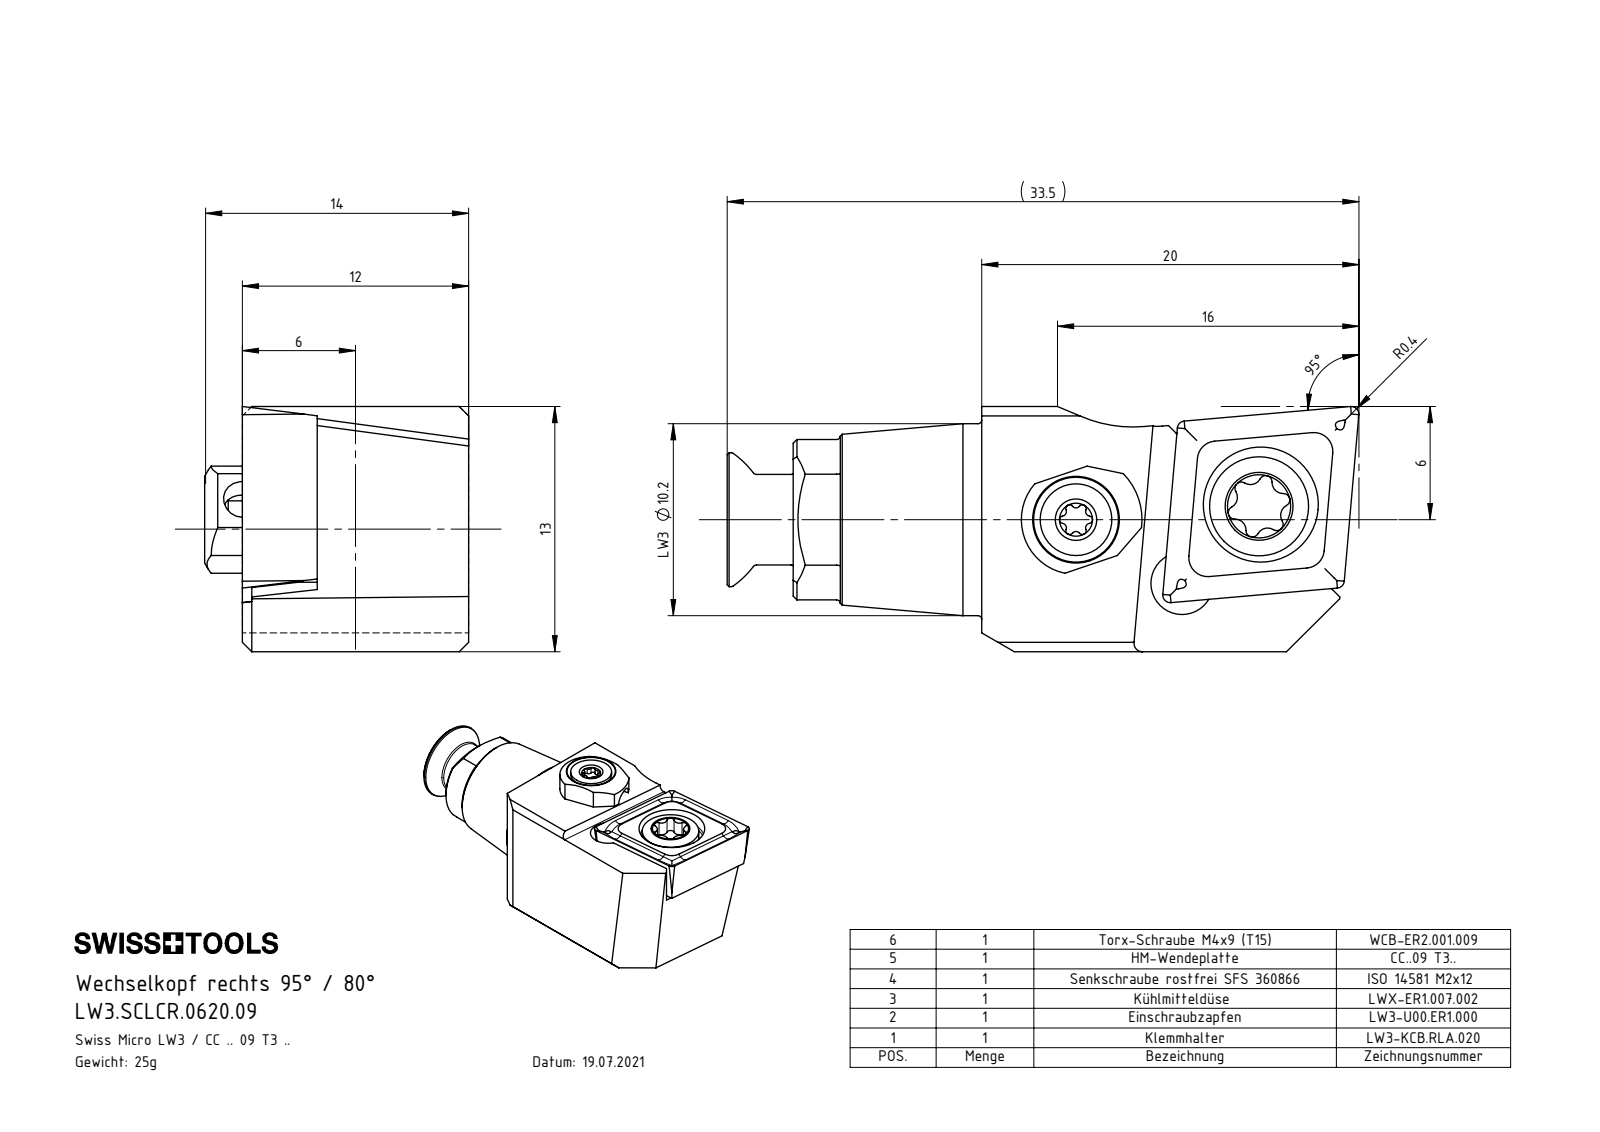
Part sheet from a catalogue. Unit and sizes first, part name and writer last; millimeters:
Units: millimetres
Overall size (bounding box): 33.4 × 14 × 13
Round holes (diameter × count): ⌀3.3 ×2, ⌀1.6 ×1, ⌀2 ×1, ⌀2.5 ×1, ⌀3 ×1, ⌀4.4 ×1, ⌀5.5 ×1, ⌀6.1 ×1
Round bosses / shafts (diameter × count): ⌀10.18 ×1, ⌀6.9 ×1, ⌀6 ×1, ⌀5.25 ×1, ⌀5 ×1, ⌀4.8 ×1, ⌀4 ×1, ⌀3.8 ×1
Partial cylindrical surfaces — rounded edges, fillets, slot ends (radius × count): R0.2 ×8, R0.24 ×6, R0.34 ×6, R0.59 ×6, R0.5 ×1, R1 ×1, R2.9 ×1, R3.5 ×1
Main face-to-face distances: 12, 8.03, 3.97, 2, 0.5, 11.5, 2.5, 3.47, 13, 13.4
Hole centre spacings: 5.78, 5.91, 6.56, 9.74, 9.83
Volume: 3 216 mm³ · Surface area: 2 735 mm²
Bodies: 6 solids, 257 faces (71 planar, 79 cylindrical, 107 other)
Part name (STEP PRODUCT): LW3-U00.ER1.000_B; CCMT09T304; ISO 14581 - M2x12; WCB-ER2.001.009_A (+3 more)
STEP written by: SolidWorks 2022 (CONFIG_CONTROL_DESIGN)
